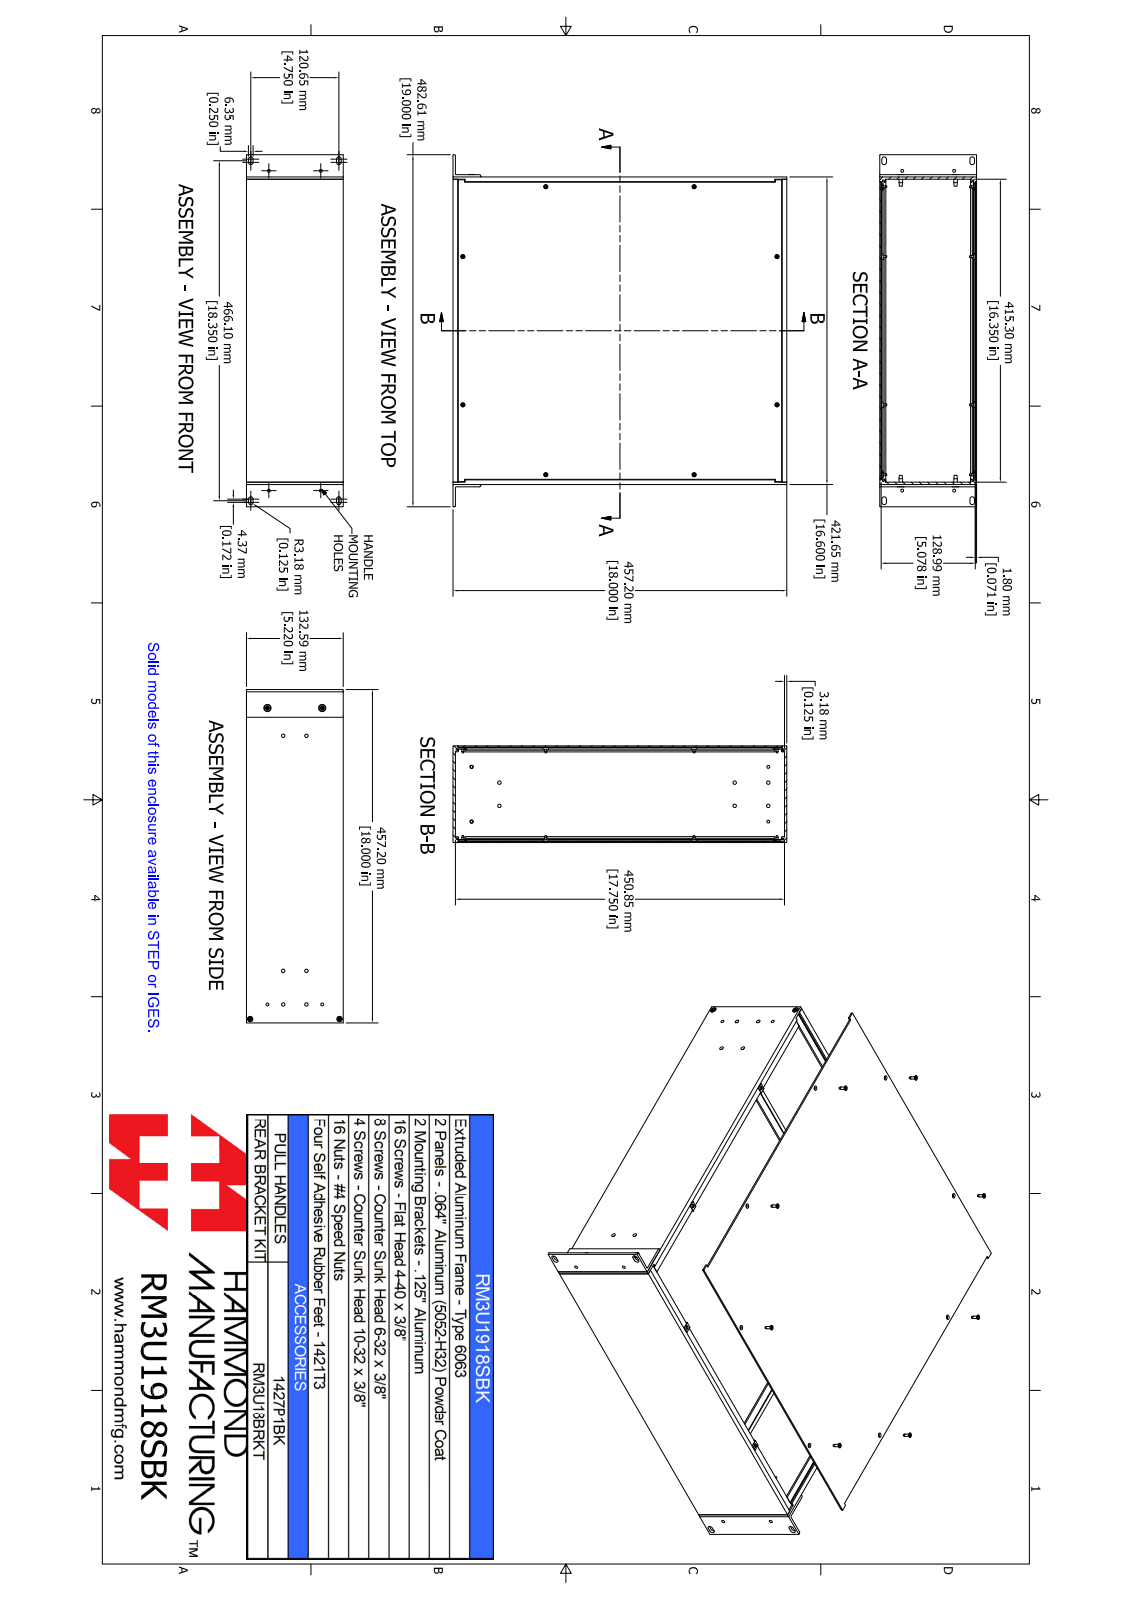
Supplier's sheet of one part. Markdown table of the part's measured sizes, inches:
| quantity | value |
| --- | --- |
| part name | RM3U1918SBK |
| STEP written by | SolidWorks 2021 (AUTOMOTIVE_DESIGN) |
| units | inches |
| bodies | 52 solids, 1364 faces (636 planar, 232 cylindrical, 496 other) |
| overall size | 19 × 18 × 5.22 |
| volume | 96.88 in³ |
| surface area | 2 119 in² |
| round holes (diameter × count) | 0.118 × 9, 0.098 × 8, 0.157 × 8, 0.157 × 8, 0.188 × 6, 0.159 × 4, 0.169 × 4, 0.169 × 4, 0.197 × 2 |
| round bosses / shafts (diameter × count) | 0.214 × 11, 0.112 × 9, 0.238 × 4, 0.138 × 4, 0.333 × 2, 0.19 × 2 |
| partial cylindrical surfaces (radius × count) | 0.125 × 16, 0.039 × 14, 0.037 × 8, 0.049 × 8, 0.05 × 8, 0.038 × 4, 0.079 × 2 |
| main face-to-face distances | 0.071, 5.149, 5.22, 5.078, 0.125, 16.476, 0.125, 16.601, 16.35, 18 |
| hole center spacings | 8, 13.031, 5.851, 5.852, 12.594, 17.152, 1.224, 1.25 |
